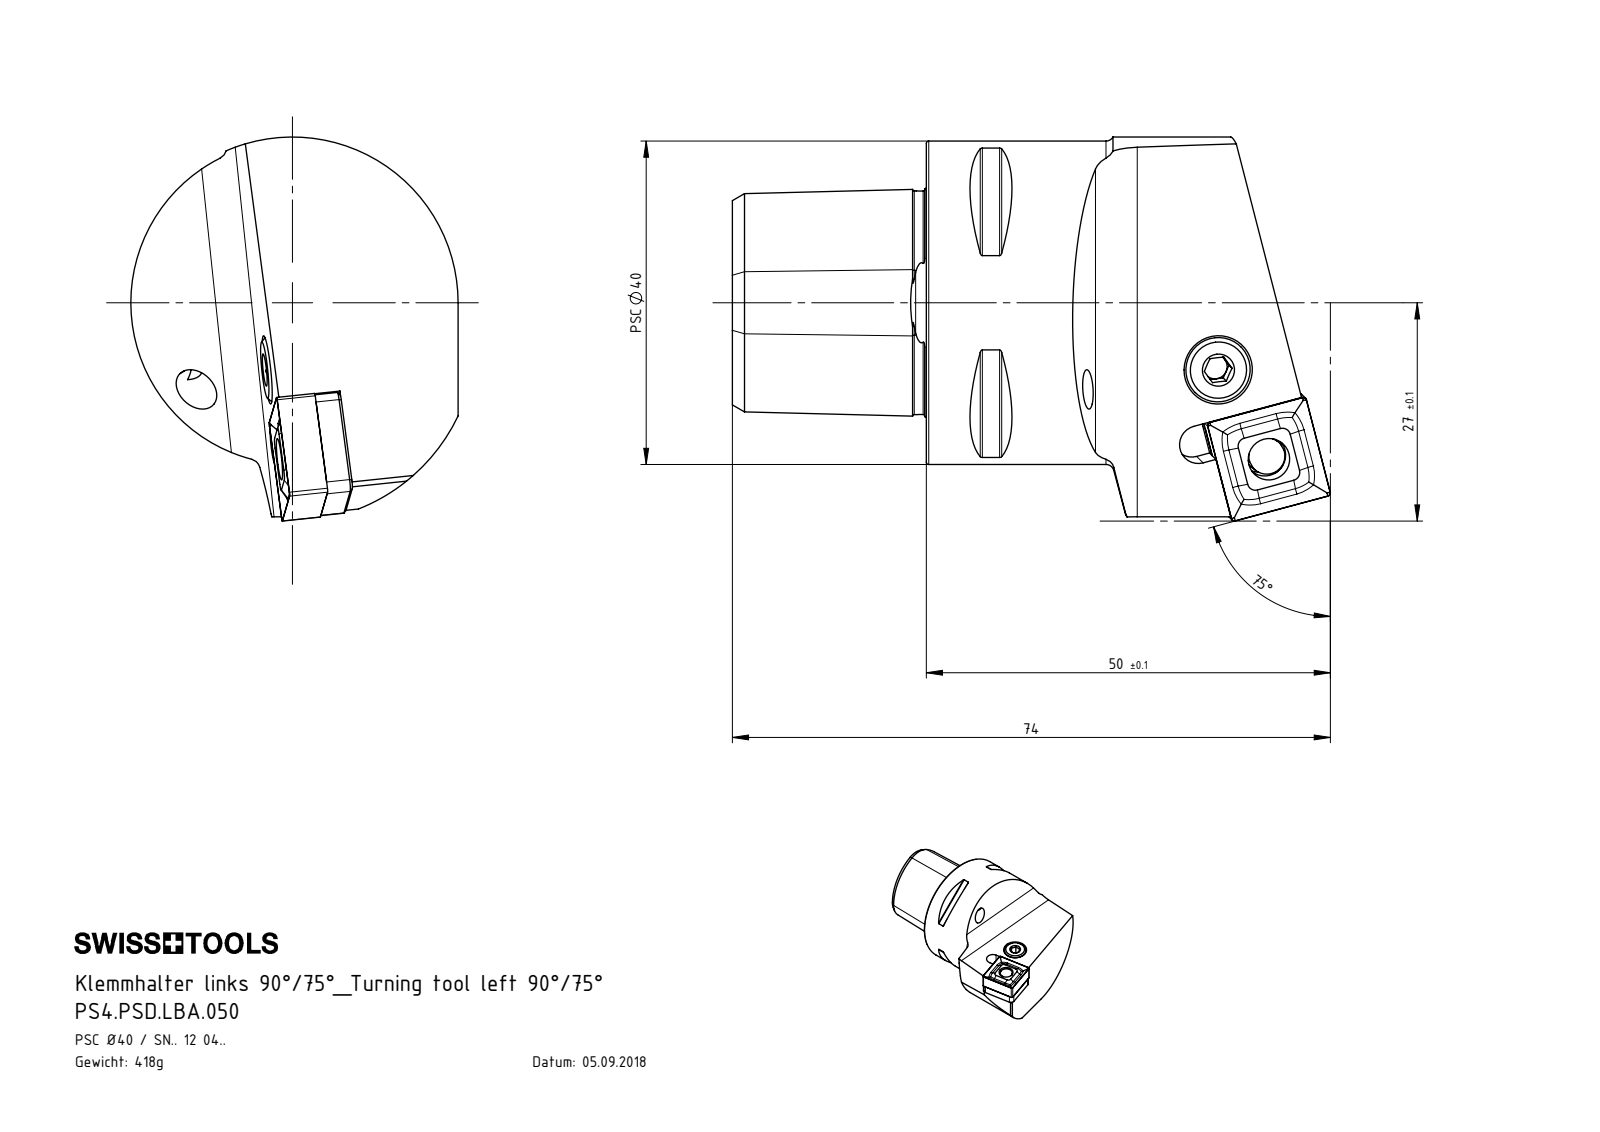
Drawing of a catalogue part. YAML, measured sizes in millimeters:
part_name: "SNMG120404; KVT_MB_600_050; WCD-ER4.101.017_A; PS4.PSD.LBA.050 (+4 more)"
step_written_by: "SolidWorks 2017 (AUTOMOTIVE_DESIGN)"
units: millimeters
bodies: {solids: 8, faces: 261, planar: 89, cylindrical: 55, other: 117}
overall_size: [74, 47.5, 40.5]
volume: 52619
surface_area: 15432
round_holes:
  - {diameter: 4, count: 2}
  - {diameter: 4.2, count: 2}
  - {diameter: 4.6, count: 1}
  - {diameter: 5.16, count: 1}
  - {diameter: 6.4, count: 1}
  - {diameter: 7, count: 1}
  - {diameter: 8.4, count: 1}
  - {diameter: 12.5, count: 1}
  - {diameter: 18, count: 1}
  - {diameter: 20, count: 1}
round_bosses_or_shafts:
  - {diameter: 40, count: 1}
  - {diameter: 8, count: 1}
  - {diameter: 7.9, count: 1}
  - {diameter: 6.4, count: 1}
  - {diameter: 5, count: 1}
  - {diameter: 4.5, count: 1}
  - {diameter: 3.55, count: 1}
partial_cylinders:
  - {radius: 0.3, count: 8}
  - {radius: 0.4, count: 4}
  - {radius: 1.2, count: 4}
  - {radius: 2.5, count: 2}
  - {radius: 3.2, count: 2}
  - {radius: 0.8, count: 1}
  - {radius: 2.2, count: 1}
  - {radius: 2.35, count: 1}
face_to_face_distances: [3.18, 24, 12.22, 4.47, 15.52, 12.7, 4.46, 3.19, 7.65, 3.17]
hole_center_spacings: [12.8, 23.5]
